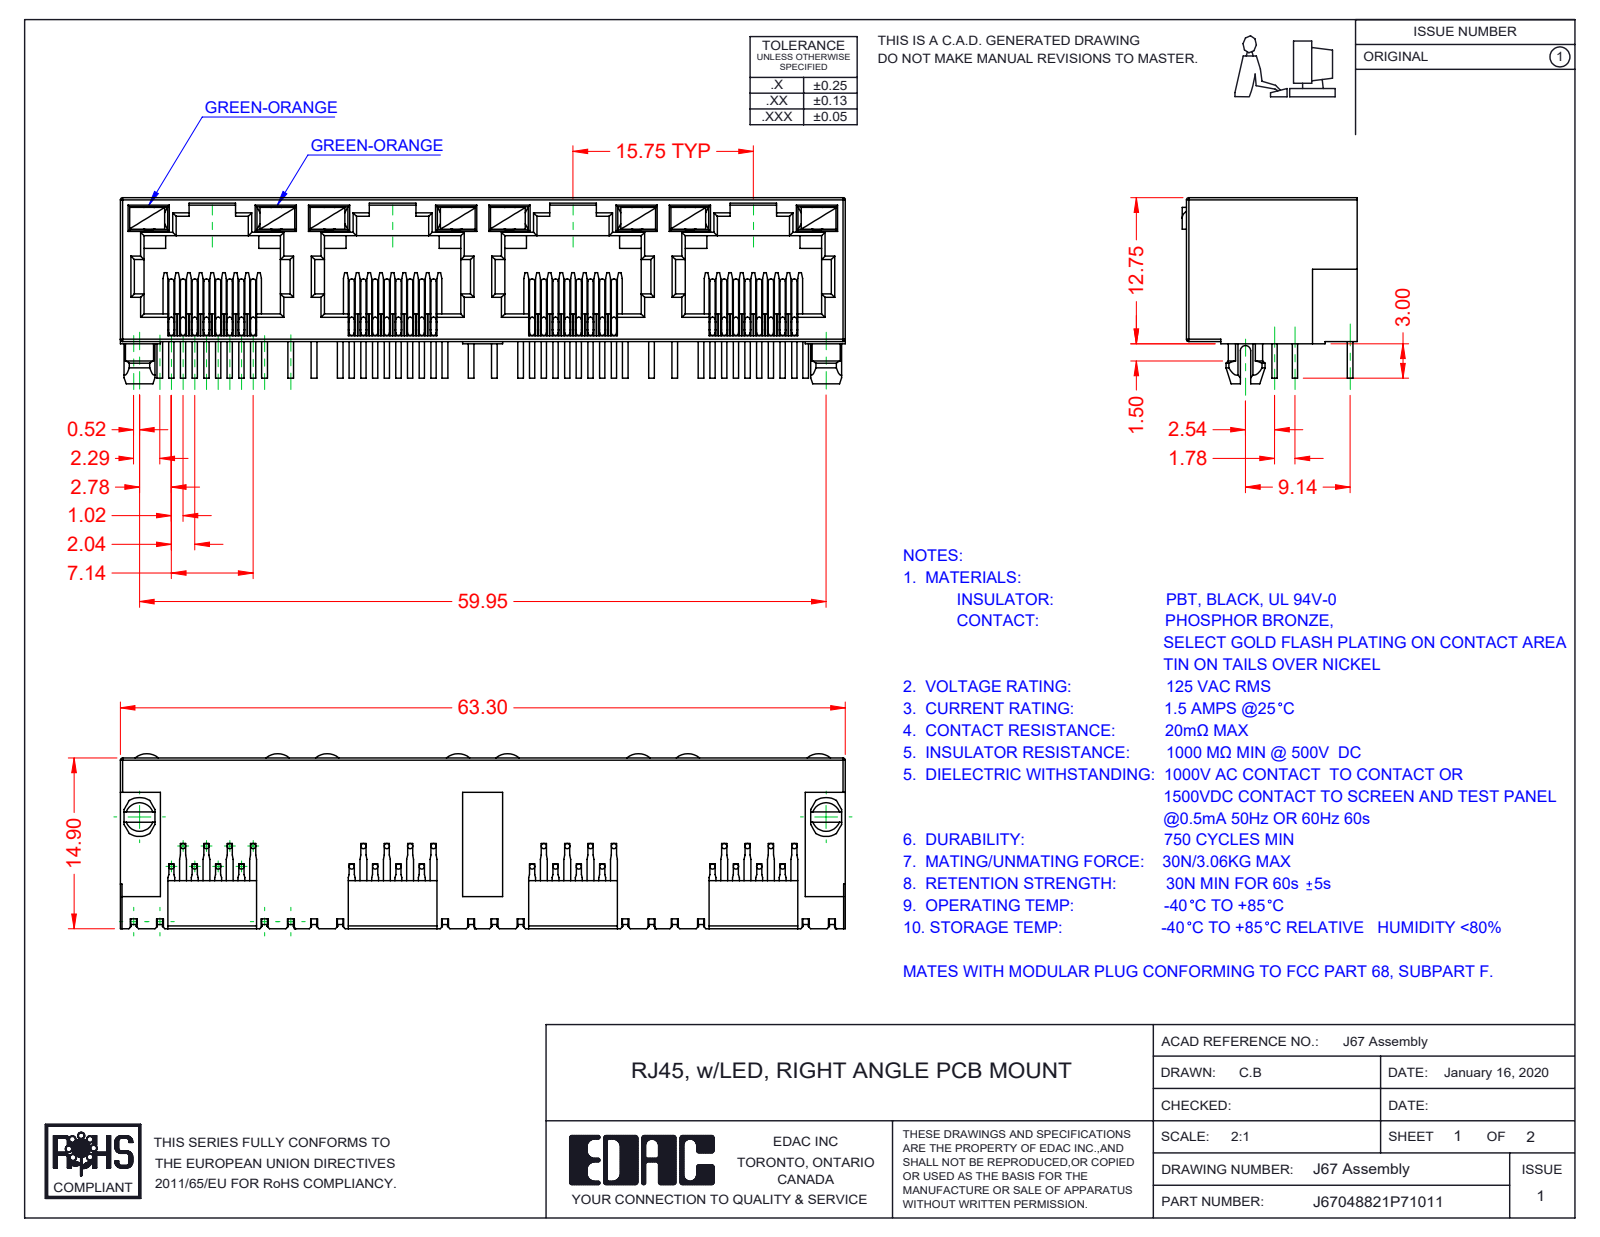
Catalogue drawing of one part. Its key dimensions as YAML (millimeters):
part_name: "67 LED LH_7-Green-Orange; 67 Contacts; 67 Insulator; J67048822P77011 (+1 more)"
step_written_by: "SolidWorks 2016 (CONFIG_CONTROL_DESIGN)"
units: millimeters
bodies: {solids: 41, faces: 2481, planar: 1781, cylindrical: 492, other: 208}
overall_size: [63.3, 16.25, 15.28]
volume: 5159
surface_area: 11573
round_bosses_or_shafts:
  - {diameter: 0.46, count: 96}
partial_cylinders:
  - {radius: 0.2, count: 66}
  - {radius: 0.3, count: 29}
  - {radius: 0.45, count: 9}
  - {radius: 1.55, count: 8}
  - {radius: 1.5, count: 2}
  - {radius: 1.7, count: 2}
  - {radius: 0.35, count: 1}
  - {radius: 1, count: 1}
face_to_face_distances: [0.5, 12.55, 1.89, 0.89, 10, 15.75, 1, 1.39, 11, 11.89]
